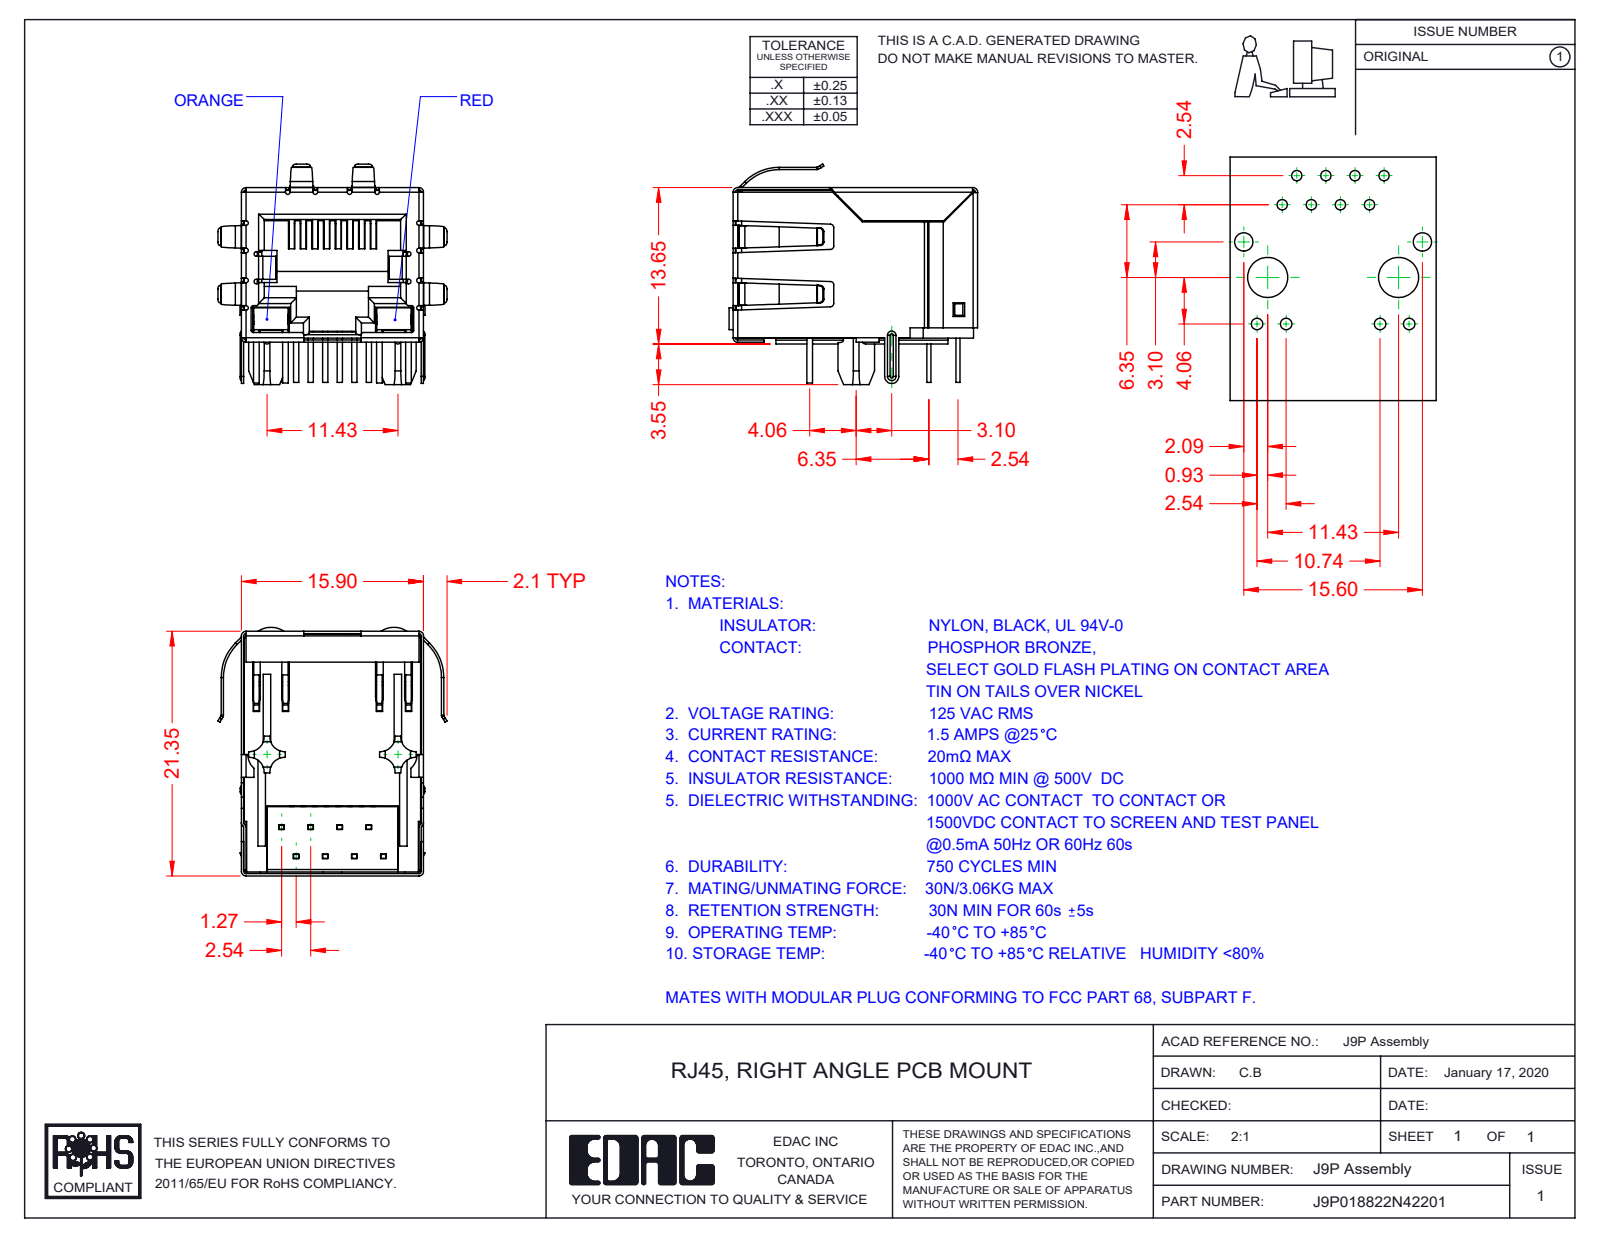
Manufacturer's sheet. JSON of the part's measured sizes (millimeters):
{"part_name": "9P-LED Insulator; 9P-LED LED RH_2-Red; 9P-LED Contacts; J9P018822N42202 (+4 more)", "step_written_by": "SolidWorks 2016 (CONFIG_CONTROL_DESIGN)", "units": "millimeters", "bodies": {"solids": 13, "faces": 1472, "planar": 1042, "cylindrical": 336, "other": 94}, "overall_size": [21.7, 20, 19.25], "volume_mm3": 2687, "surface_area_mm2": 7515, "partial_cylinders_radius": [[0.2, 39], [0.5, 22], [0.3, 20], [0.4, 16], [1.3, 8], [0.23, 5], [0.11, 4], [0.31, 4]], "face_to_face_distances": [15.45, 15.7, 15.65, 0.35, 0.54, 15.5, 12.36, 0.6, 1.4, 0.59]}
